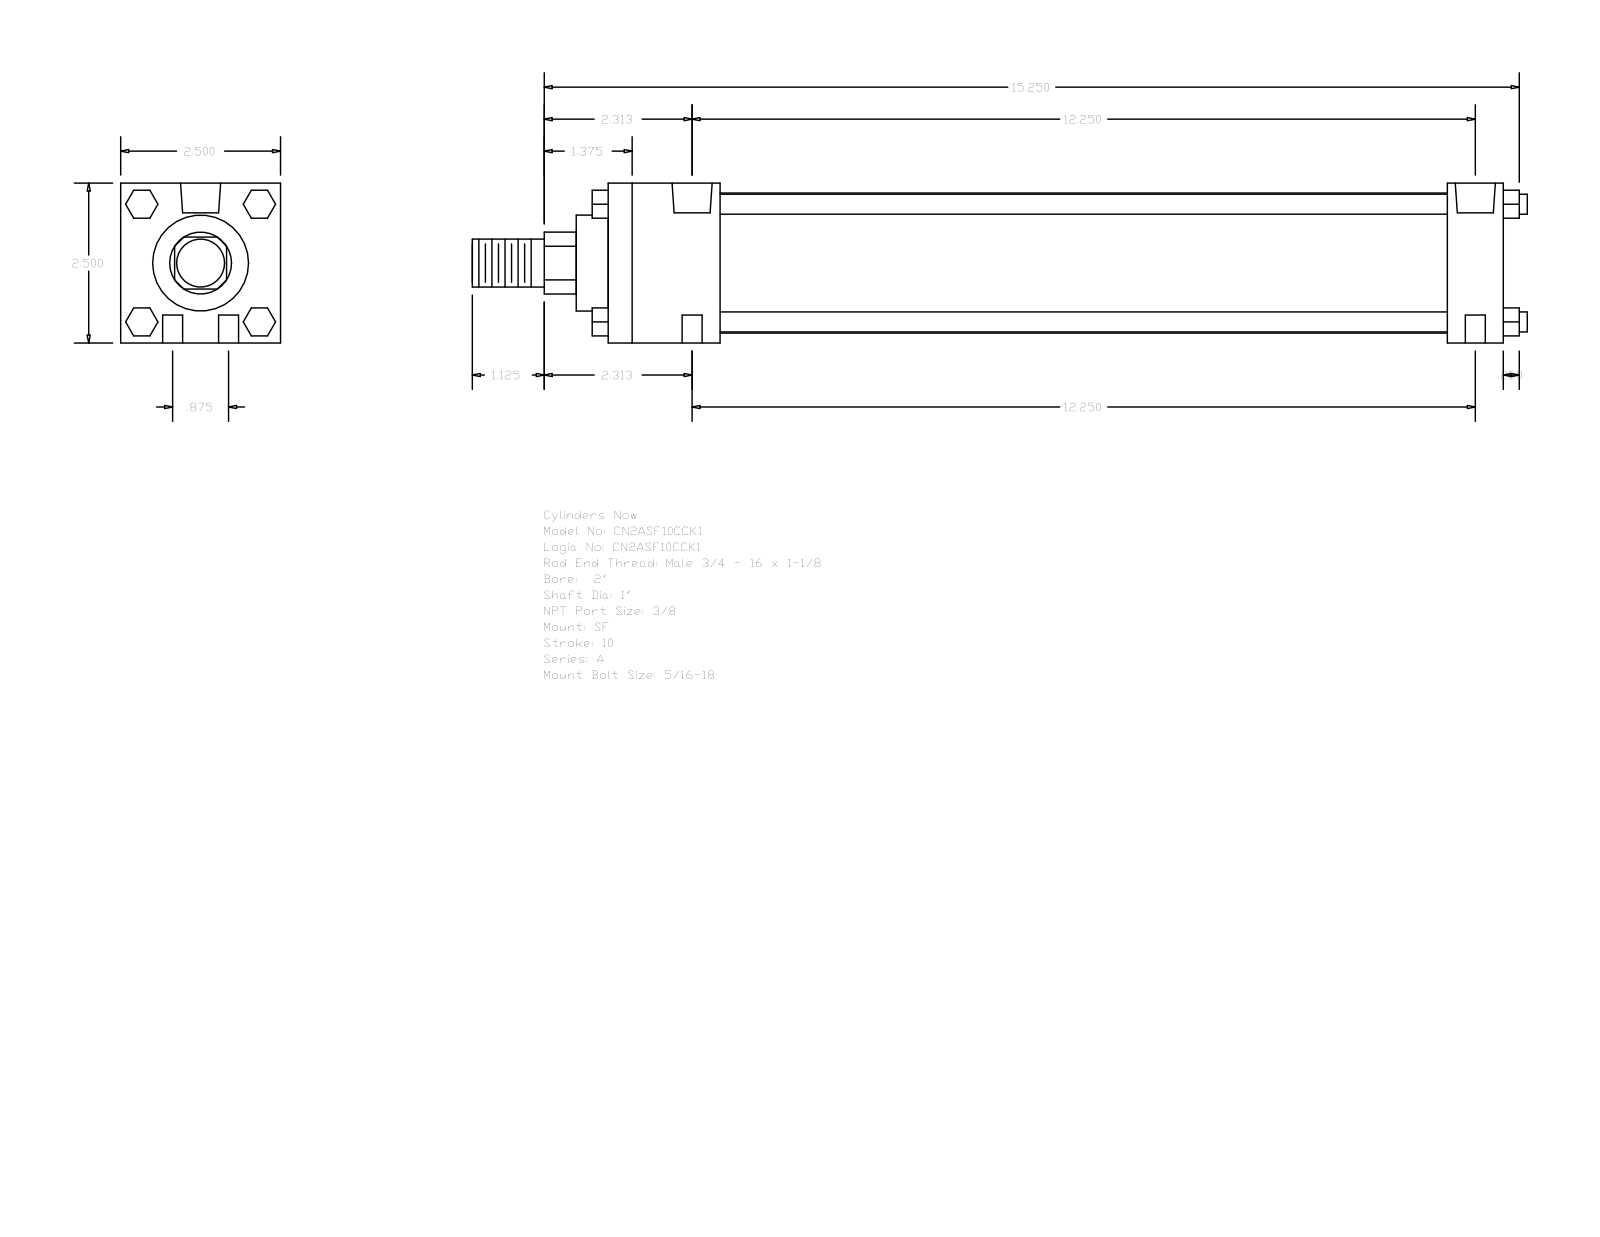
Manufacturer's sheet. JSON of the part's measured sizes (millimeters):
{"part_name": "A_SF__0200_1", "step_written_by": "GSSL Pune (CONFIG_CONTROL_DESIGN)", "units": "millimeters", "bodies": {"solids": 0, "faces": 124, "planar": 94, "cylindrical": 30, "other": 0}, "overall_size": [419.1, 63.5, 63.5], "round_holes": [[7.94, 4], [5.56, 2], [15.93, 2]], "round_bosses_or_shafts": [[7.94, 4], [55.63, 1], [38.1, 1], [25.4, 1], [19.05, 1]], "partial_cylinders_radius": [[12.29, 1]], "face_to_face_distances": [63.5, 355.6, 333.37, 22.23, 44.45, 288.92, 311.15, 12.7, 368.3, 6.35], "hole_center_spacings": [11.11, 311.35, 311.15, 22.22, 311.94, 305.58]}
